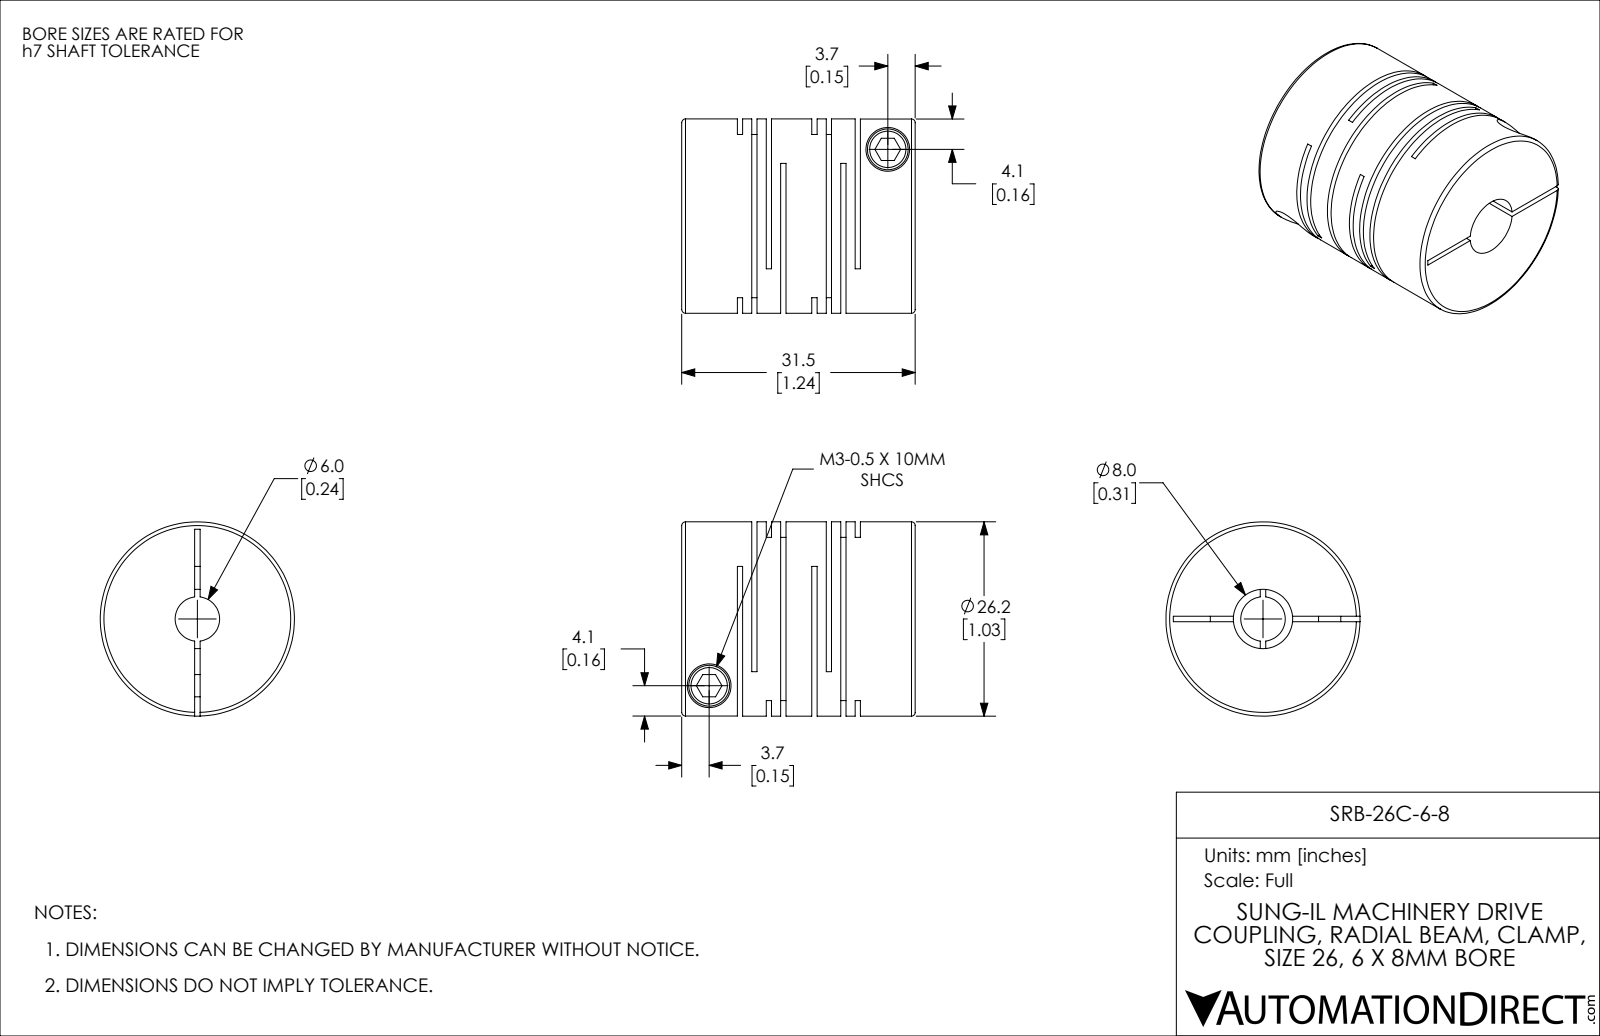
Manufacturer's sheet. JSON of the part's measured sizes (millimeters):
{"part_name": "SRB-26C-6-8", "step_written_by": "SolidWorks 2021 (CONFIG_CONTROL_DESIGN)", "units": "millimeters", "bodies": {"solids": 1, "faces": 114, "planar": 60, "cylindrical": 42, "other": 12}, "overall_size": [31.5, 26.2, 26.2], "volume_mm3": 12804, "surface_area_mm2": 11150, "round_holes": [[3, 2], [5.9, 2], [6, 1], [8, 1]], "round_bosses_or_shafts": [[5.5, 2], [26.2, 1]], "face_to_face_distances": [1.95, 10.05, 0.71, 3.9, 8.1, 12, 1.24, 2.66, 9.34, 13.95]}
